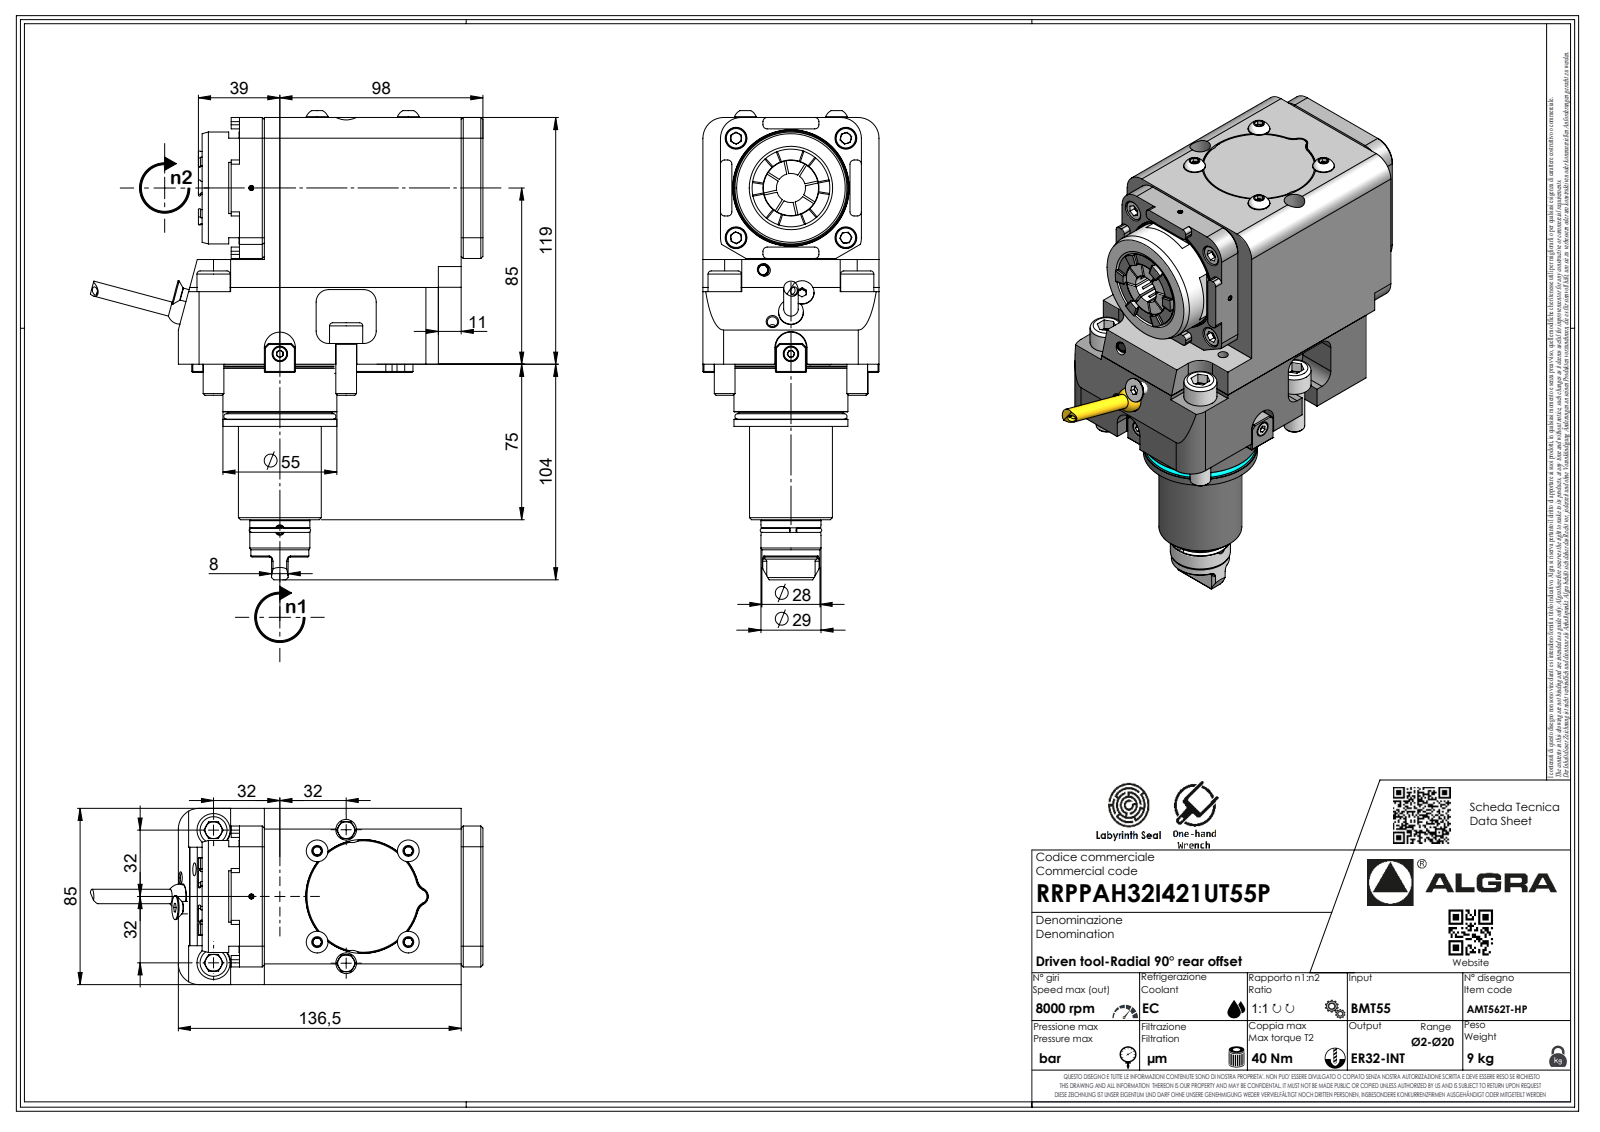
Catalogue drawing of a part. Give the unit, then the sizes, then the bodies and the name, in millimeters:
Units: millimetres
Overall size (bounding box): 226.3 × 189.45 × 85
Round holes (diameter × count): ⌀2.1 ×1, ⌀4 ×1
Round bosses / shafts (diameter × count): ⌀10.5 ×4, ⌀10 ×4, ⌀16 ×2, ⌀55 ×1, ⌀54.6 ×1, ⌀54 ×1, ⌀50.2 ×1, ⌀40 ×1
Partial cylindrical surfaces — rounded edges, fillets, slot ends (radius × count): R2 ×23, R10 ×10, R0.33 ×7, R0.52 ×7, R3.7 ×7, R4 ×4, R1 ×2, R8.25 ×2
Main face-to-face distances: 85, 119, 11, 21.5, 10.5, 30, 68, 68.5, 50.5, 8.5
Volume: 1 372 000 mm³ · Surface area: 96 153 mm²
Bodies: 1 solid, 676 faces (415 planar, 107 cylindrical, 154 other)
Part name (STEP PRODUCT): RRPPAH32I421UT55P
STEP written by: SolidWorks 2023 (AUTOMOTIVE_DESIGN)
